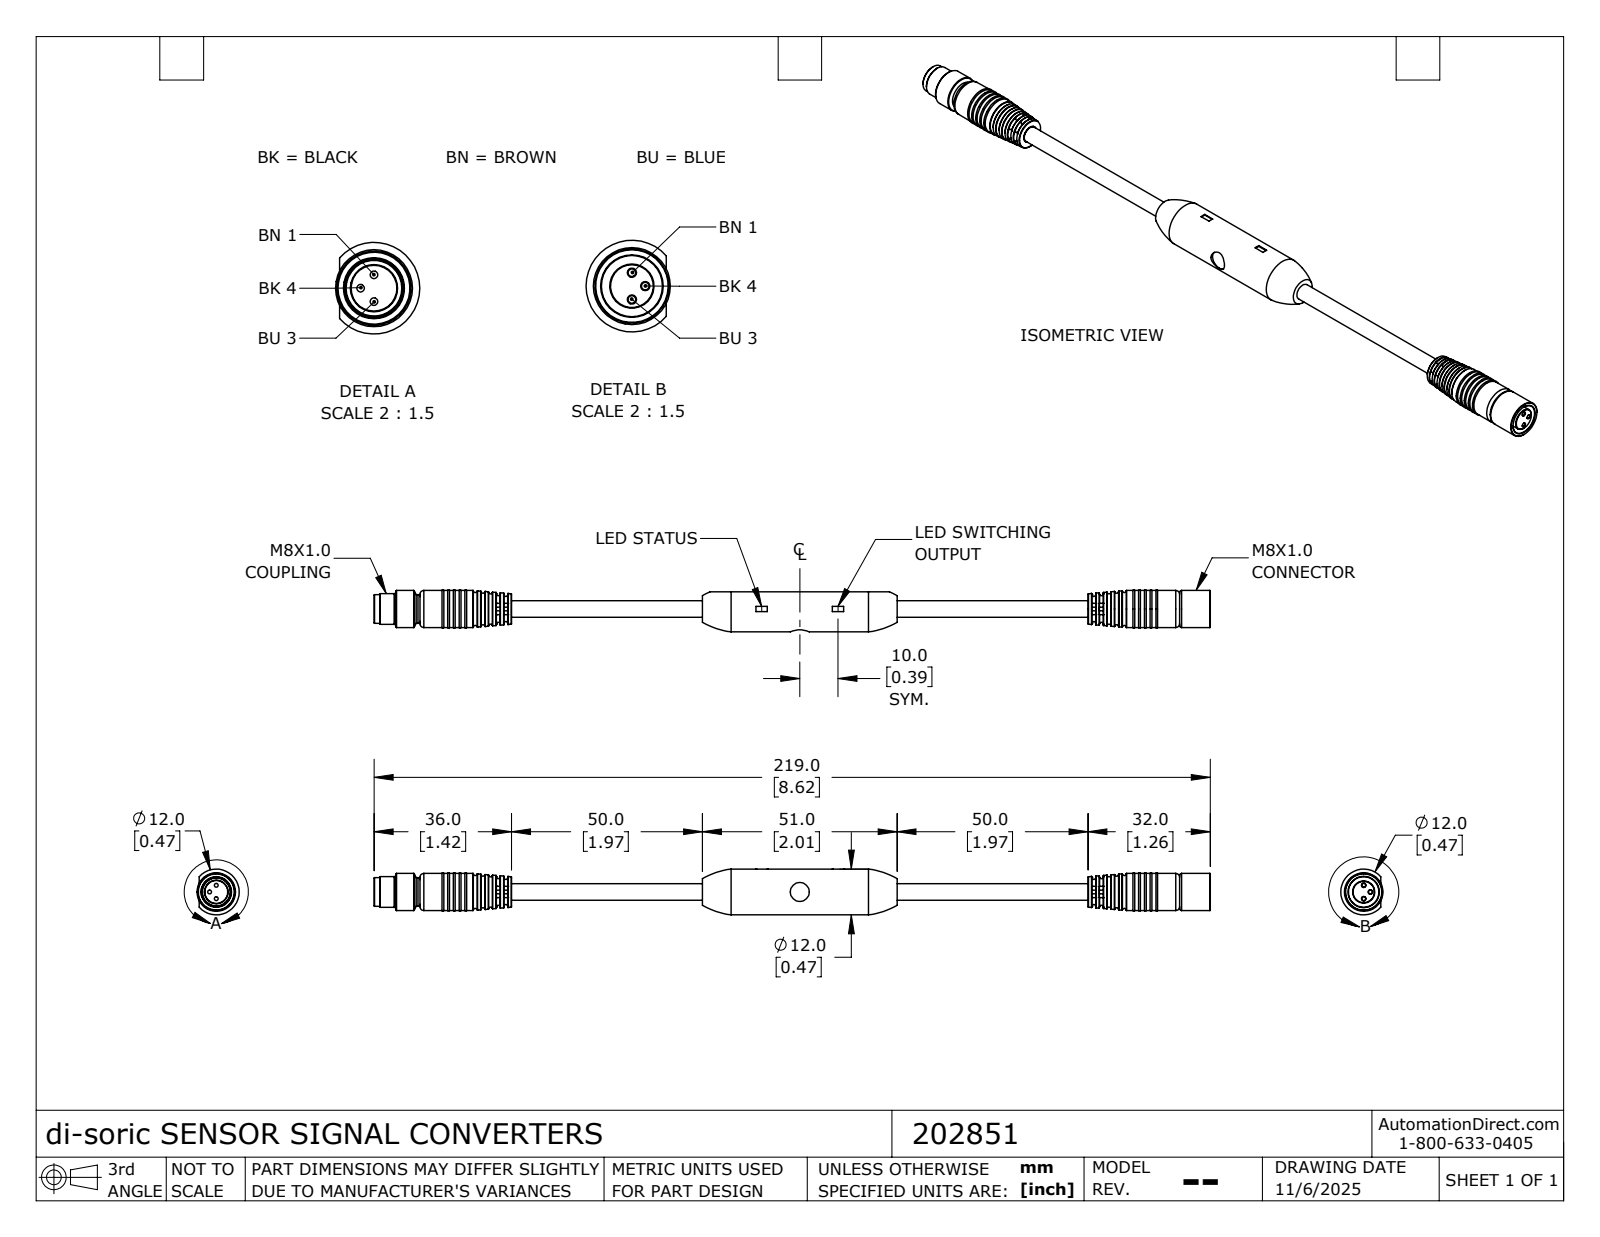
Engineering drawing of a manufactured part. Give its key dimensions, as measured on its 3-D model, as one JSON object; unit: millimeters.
{"part_name": "TKHM-Z_TSM-Z_U", "step_written_by": "SolidWorks 2024 (AUTOMOTIVE_DESIGN)", "units": "millimeters", "bodies": {"solids": 1, "faces": 260, "planar": 132, "cylindrical": 42, "other": 86}, "overall_size": [219, 12, 12], "volume_mm3": 10010, "surface_area_mm2": 7758, "round_holes": [[1, 3], [1.43, 3], [1.72, 3], [3, 1], [4.6, 1], [5, 1], [6, 1], [8, 1]], "round_bosses_or_shafts": [[9.7, 1], [7.9, 1], [7.5, 1], [5.8, 1], [4.5, 1], [4.3, 1]], "partial_cylinders_radius": [[6, 1]], "face_to_face_distances": [1, 2, 3, 155, 154, 156, 51, 157, 153, 6], "hole_center_spacings": [1.6, 0.84, 1, 1.46, 1.75, 1.01, 1.1, 1.73]}
